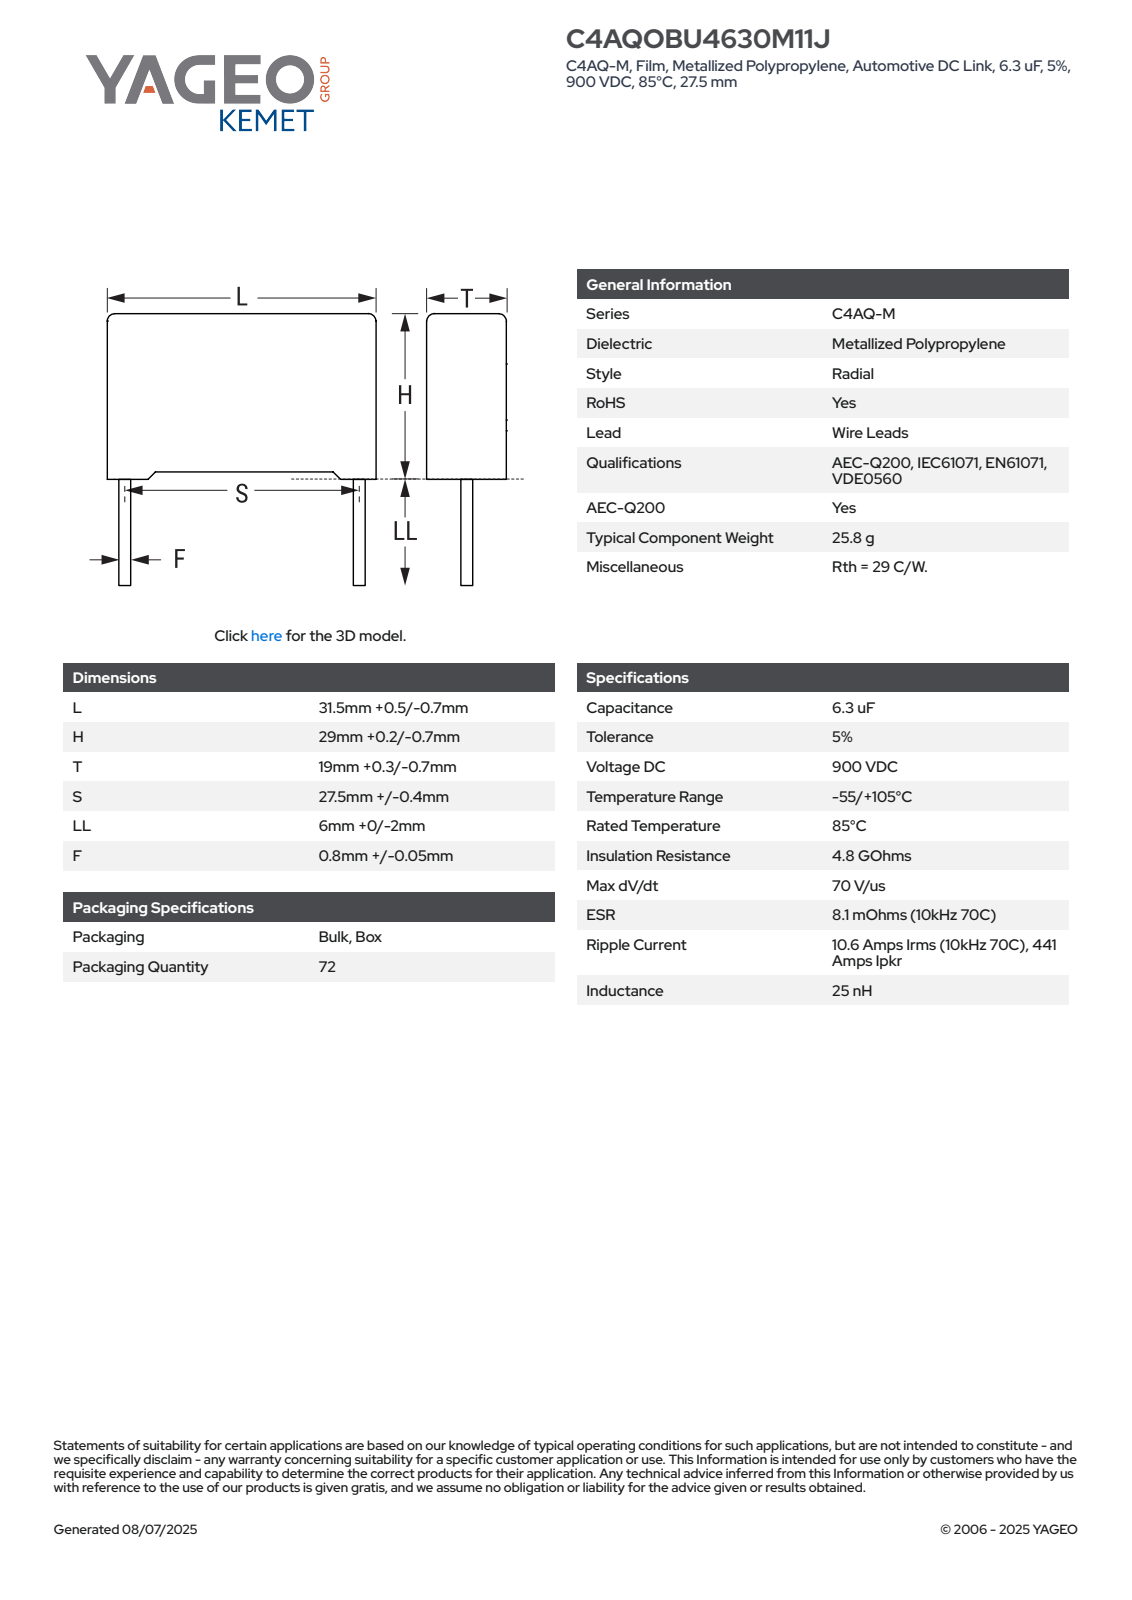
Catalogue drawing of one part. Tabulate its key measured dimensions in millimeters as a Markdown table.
| quantity | value |
| --- | --- |
| part name | CFR_RB2CFP_31.5X29X19_L32H29.2T19.3S27.5LL6F0.85 |
| STEP written by | SolidWorks 2014 (AUTOMOTIVE_DESIGN) |
| units | millimeters |
| bodies | 4 solids, 85 faces (77 planar, 8 cylindrical, 0 other) |
| overall size | 35.2 × 32 × 19.3 |
| volume | 17 500 mm³ |
| surface area | 4 315 mm² |
| round bosses / shafts (diameter × count) | 0.85 × 2 |
| partial cylindrical surfaces (radius × count) | 0.5 × 4 |
| main face-to-face distances | 19.3, 32, 28.19, 28.45, 0.75, 1.01, 29.2, 1.07, 30.93, 19.31 |
